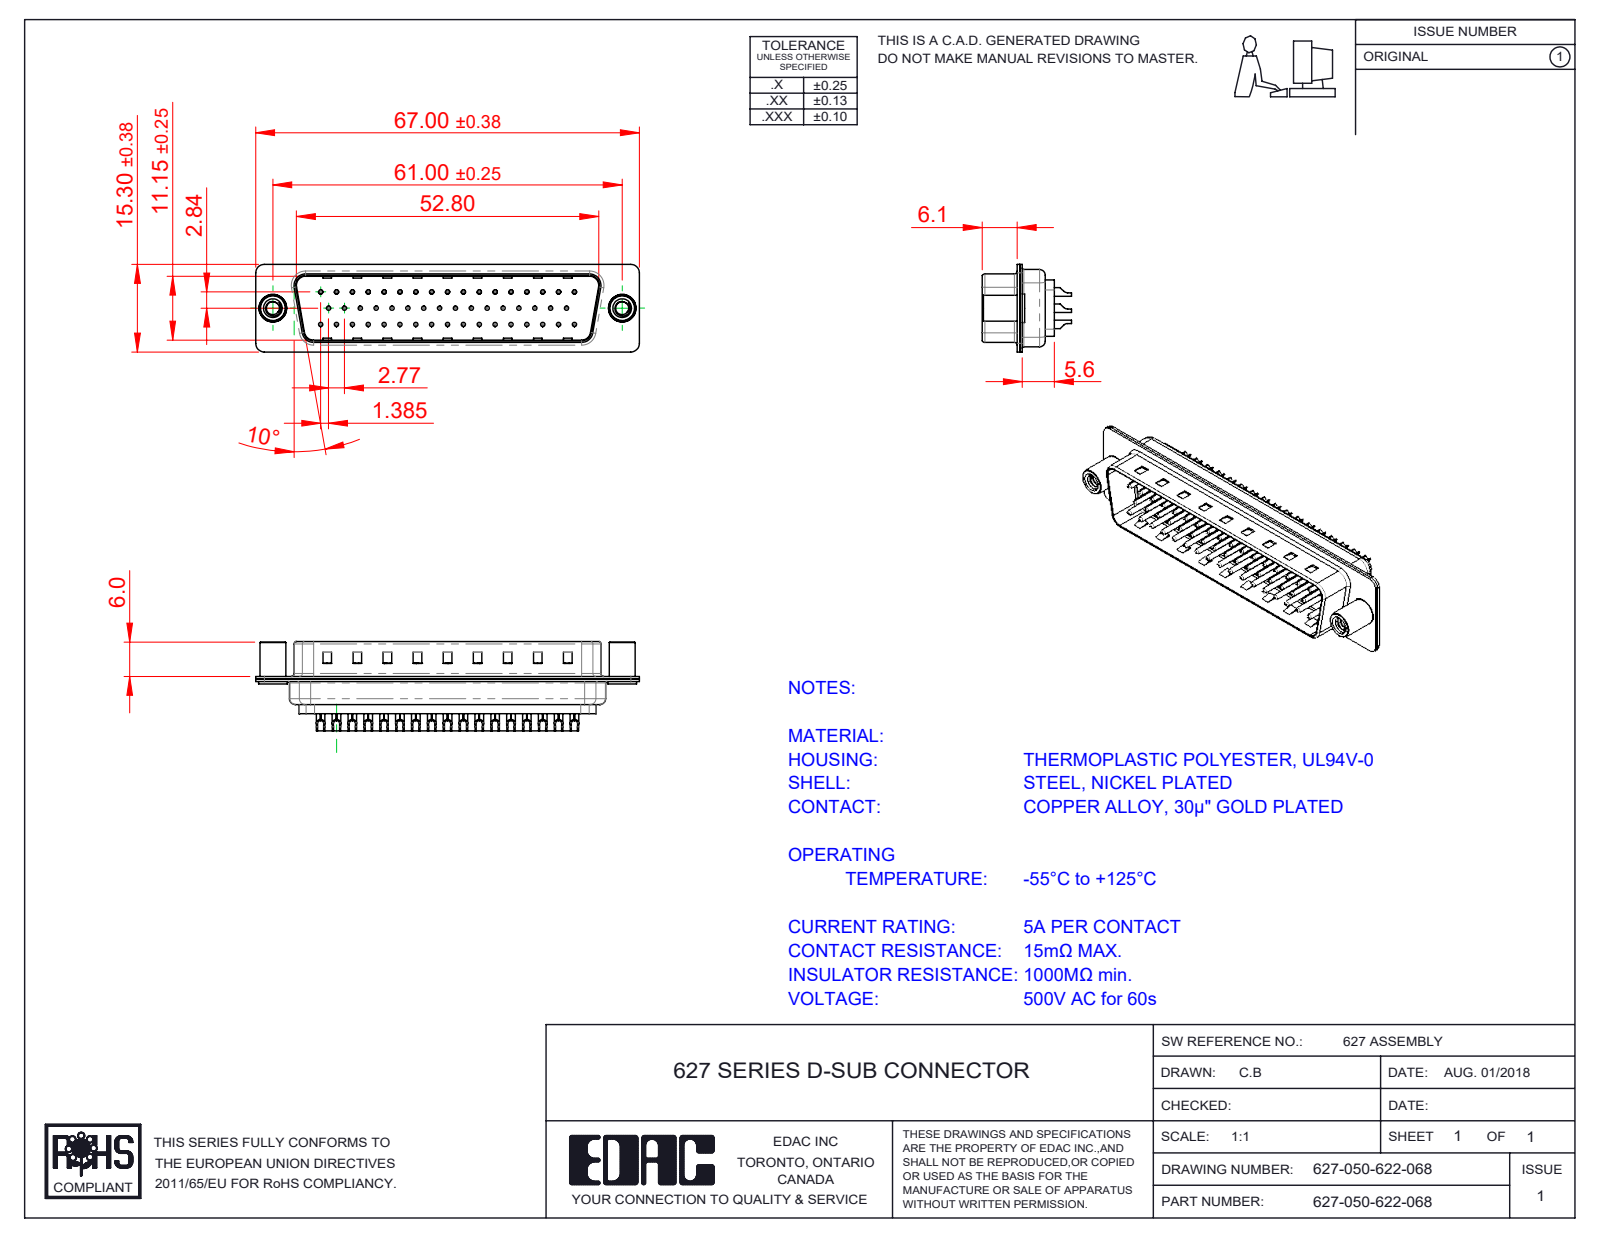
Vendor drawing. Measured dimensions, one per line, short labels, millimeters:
name: 627 Contact Row 1_22L; 627-050-622-068; 627 4-40 Threaded Standoff; 627 Shell Rear_50 Contacts (+4 more)
written by: SolidWorks 2020 (CONFIG_CONTROL_DESIGN)
unit: mm
bodies: 55 solids, 3646 faces (905 planar, 1619 cylindrical, 1122 other)
size: 67 × 15.6 × 15.3
volume: 4 515 mm³; area: 12 969 mm²
holes: 58× ⌀1.6, 50× ⌀0.35, 50× ⌀1.1, 8× ⌀0.75, 8× ⌀2, 2× ⌀2.26, 2× ⌀4, 2× ⌀4.8
bosses: 50× ⌀2, 50× ⌀1.5, 50× ⌀0.75, 2× ⌀5, 2× ⌀4.9, 2× ⌀4.5
rounds: 16× R1.5, 12× R2, 8× R0.5, 8× R1.6, 7× R1, 4× R0.25, 4× R0.6, 4× R0.65
face distances: 0.4, 0.45, 11.55, 0.9, 6.05, 6.5, 0.78, 1.95, 0.77, 12.33
hole spacings: 2.77, 3.16, 5.54, 8.31, 11.08, 13.85, 16.62, 19.39
